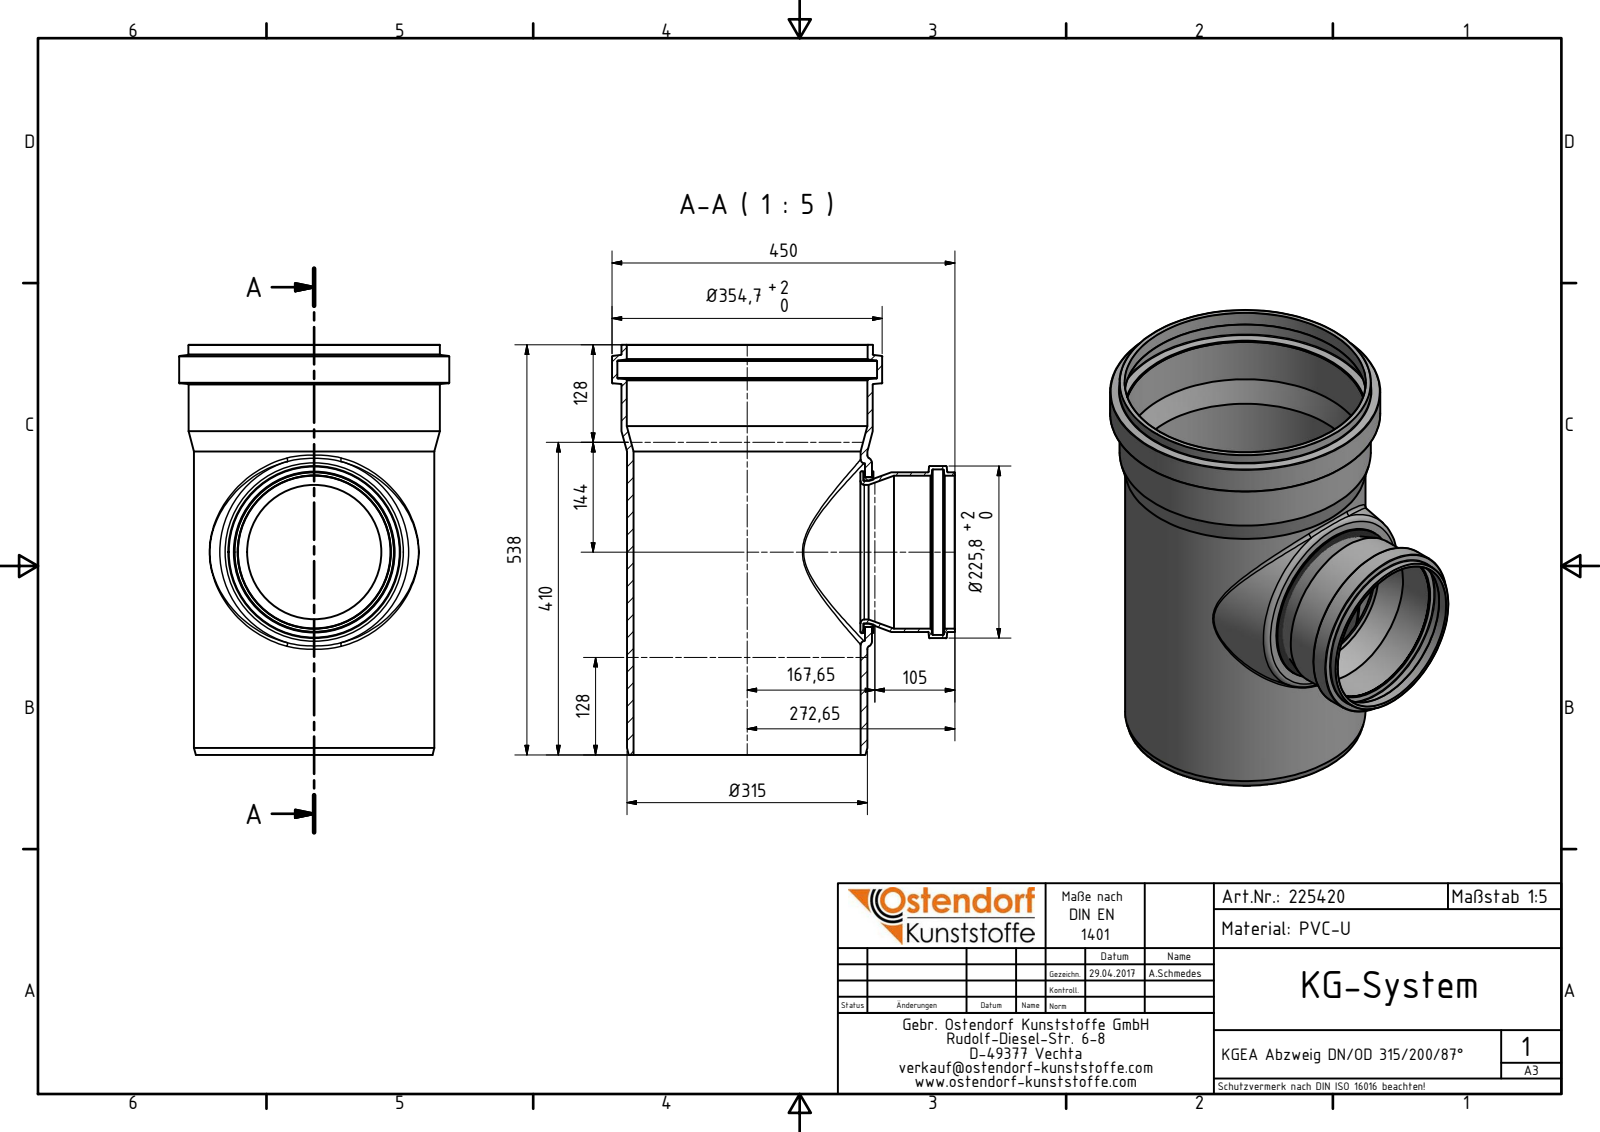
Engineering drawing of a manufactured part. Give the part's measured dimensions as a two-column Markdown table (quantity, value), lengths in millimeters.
| quantity | value |
| --- | --- |
| part name | 225420 KGEA Abzweig DN_OD 315_200_87°; 225420 KGEA Abzweig DN_OD 315_200_87° Dichtung; 225420 KGEA Abzweig DN_OD 315_200_87° Abzweig |
| STEP written by | Autodesk Inventor 2016 (AUTOMOTIVE_DESIGN) |
| units | millimeters |
| bodies | 3 solids, 83 faces (13 planar, 23 cylindrical, 47 other) |
| overall size | 538 × 450 × 354.7 |
| volume | 4 912 000 mm³ |
| surface area | 1 331 000 mm² |
| round holes (diameter × count) | 176.5 × 1, 187.5 × 1, 196.5 × 1, 200.6 × 1, 200.9 × 1, 217 × 1, 298.2 × 1, 316 × 1, 316.3 × 1, 340.9 × 1 |
| round bosses / shafts (diameter × count) | 354.7 × 1, 330.1 × 1, 329.8 × 1, 315.6 × 1, 225.8 × 1, 212 × 1, 209.7 × 1, 209.4 × 1 |
| main face-to-face distances | 2, 11, 9, 13, 4, 6, 15, 17, 538, 123.85 |
